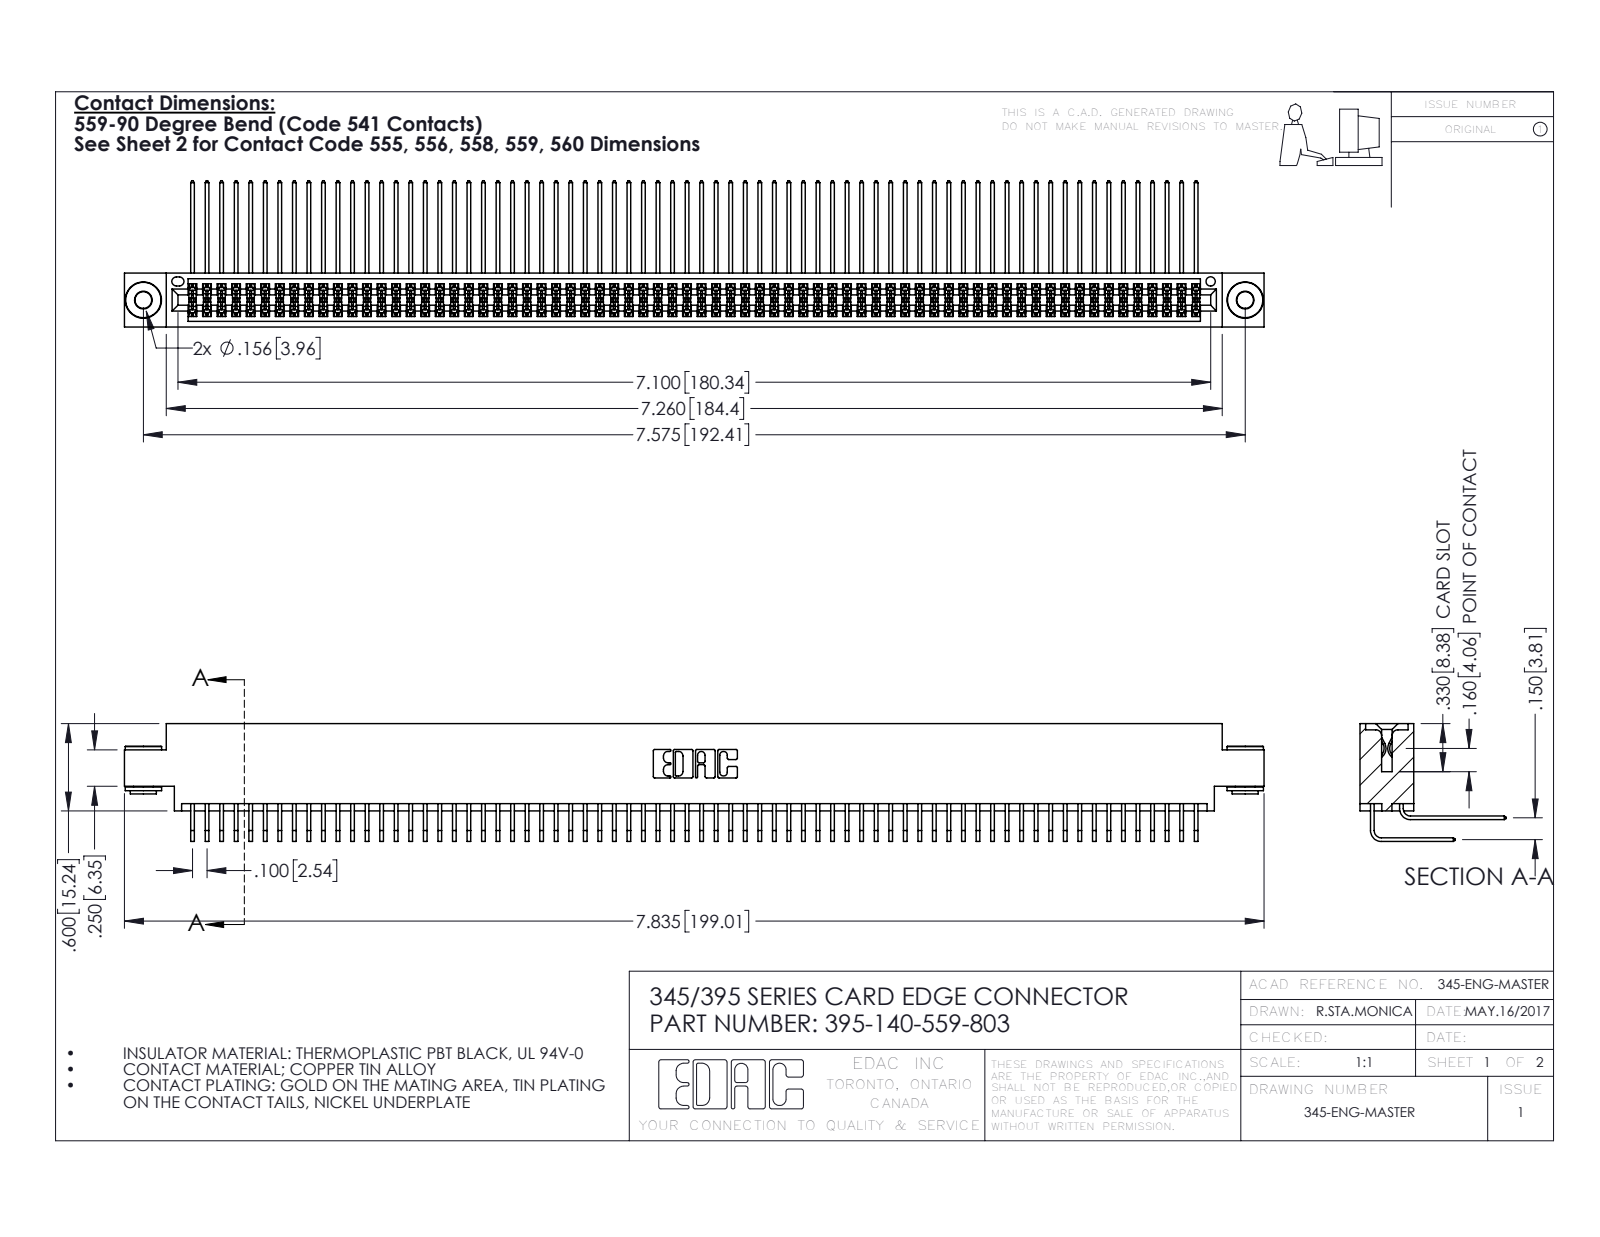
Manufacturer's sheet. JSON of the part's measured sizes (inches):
{"part_name": "345-292-001_558 559 Tail - 1; 345-250-002_345-250-002-102; 395-140-559-803; 345-292-001_559 Tail - 2 (+1 more)", "step_written_by": "SolidWorks 2016 (CONFIG_CONTROL_DESIGN)", "units": "inches", "bodies": {"solids": 143, "faces": 7448, "planar": 4994, "cylindrical": 2446, "other": 8}, "overall_size": [7.835, 1.005, 0.809], "volume_in3": 1.239, "surface_area_in2": 53.79, "round_holes": [[0.116, 2], [0.156, 2], [0.064, 1]], "round_bosses_or_shafts": [[0.25, 2], [0.18, 2], [0.136, 2]], "partial_cylinders_radius": [[0.006, 279], [0.01, 22], [0.007, 6], [0.031, 6], [0.026, 3], [0.014, 2], [0.019, 2], [0.022, 2]], "face_to_face_distances": [0.072, 0.298, 0.37, 0.2, 0.098, 0.272, 0.025, 0.225, 0.175, 0.15], "hole_center_spacings": [0.27, 7.339, 7.575]}
